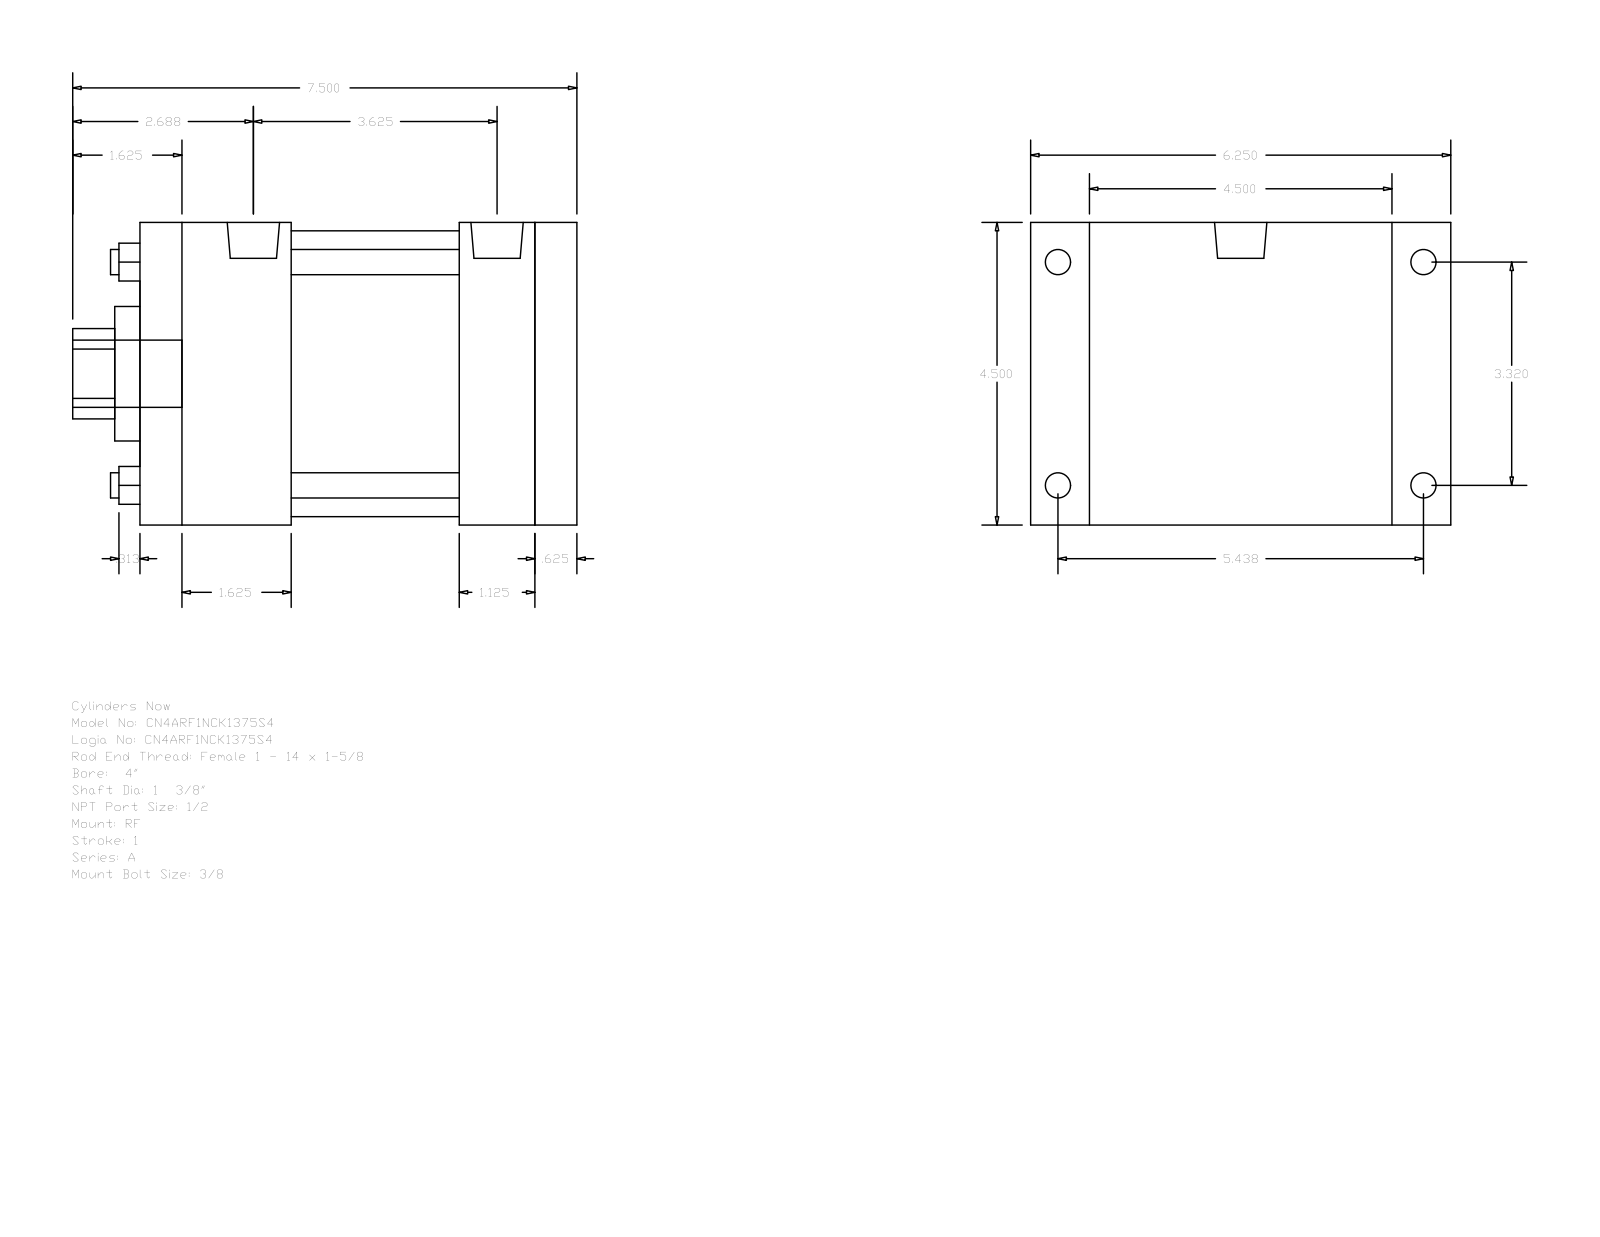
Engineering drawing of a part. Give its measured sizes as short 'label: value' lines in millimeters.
name: A_RF__0400_1.375
written by: GSSL Pune (CONFIG_CONTROL_DESIGN)
unit: mm
bodies: 0 solids, 92 faces (64 planar, 28 cylindrical, 0 other)
size: 190.5 × 158.75 × 114.3
holes: 4× ⌀9.53, 1× ⌀34.92, 1× ⌀50.8, 1× ⌀107.95
bosses: 4× ⌀9.53, 4× ⌀8.73, 2× ⌀19.77, 1× ⌀25.4
rounds: 1× R17.06
face distances: 114.3, 165.1, 15.88, 149.22, 28.57, 22.23, 136.53, 120.65, 44.45, 57.15
hole spacings: 59.62, 84.32, 119.25
